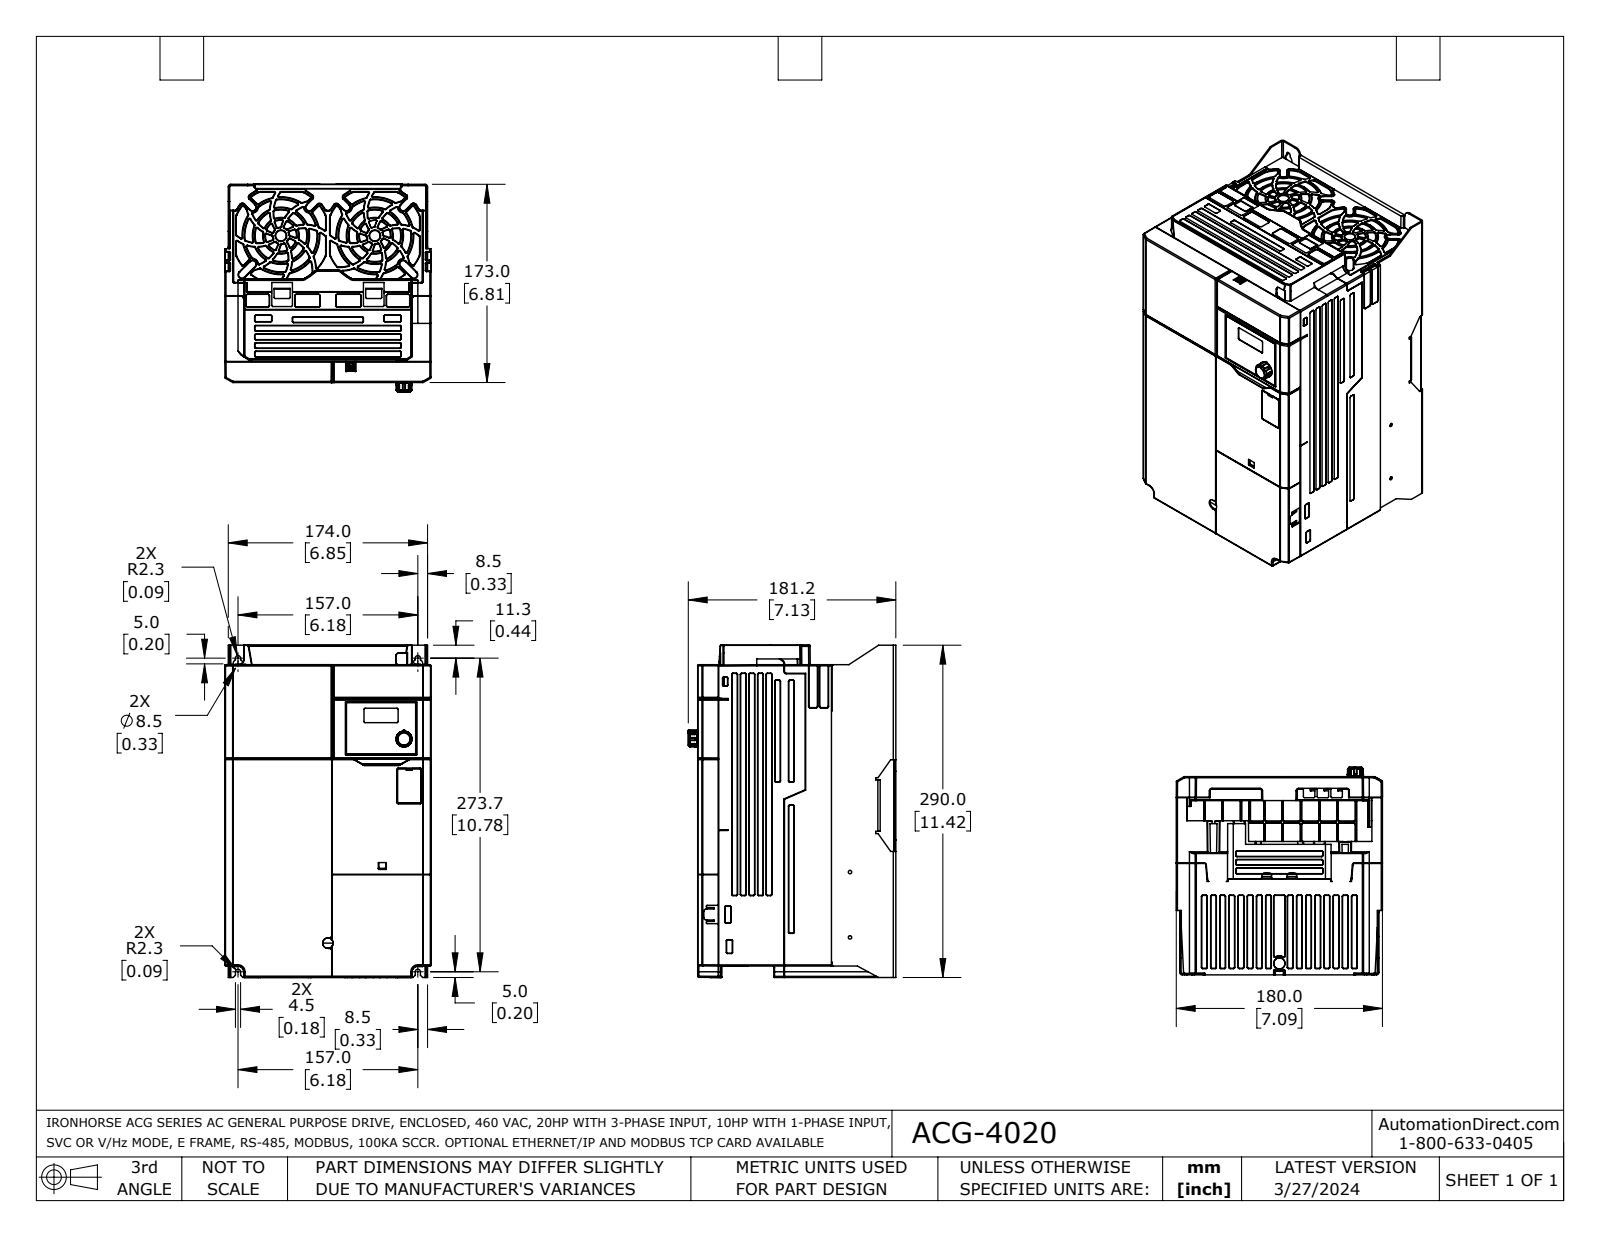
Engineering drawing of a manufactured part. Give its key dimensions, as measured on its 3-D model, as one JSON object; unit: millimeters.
{"part_name": "ACG-4020", "step_written_by": "SolidWorks 2021 (AUTOMOTIVE_DESIGN)", "units": "millimeters", "bodies": {"solids": 6, "faces": 3664, "planar": 1665, "cylindrical": 663, "other": 1336}, "overall_size": [290, 181.2, 180], "volume_mm3": 2461000, "surface_area_mm2": 552100, "round_holes": [[4.1, 4], [4.5, 3], [5.5, 3], [3, 2], [8.5, 2], [1, 1], [9.2, 1], [12, 1]], "round_bosses_or_shafts": [[9.8, 2], [8.3, 2], [5, 2], [14, 1], [13.8, 1], [8.5, 1], [8, 1], [6.6, 1]], "partial_cylinders_radius": [[1, 124], [0.2, 108], [0.5, 95], [0.3, 36], [2, 14], [5, 12], [2.2, 9], [4.5, 6]], "face_to_face_distances": [1.4, 173, 171.6, 11.5, 168.5, 157, 3, 177, 8.5, 165.5], "hole_center_spacings": [11, 22.7, 24, 35, 46, 46.6, 57.6, 68.6]}
